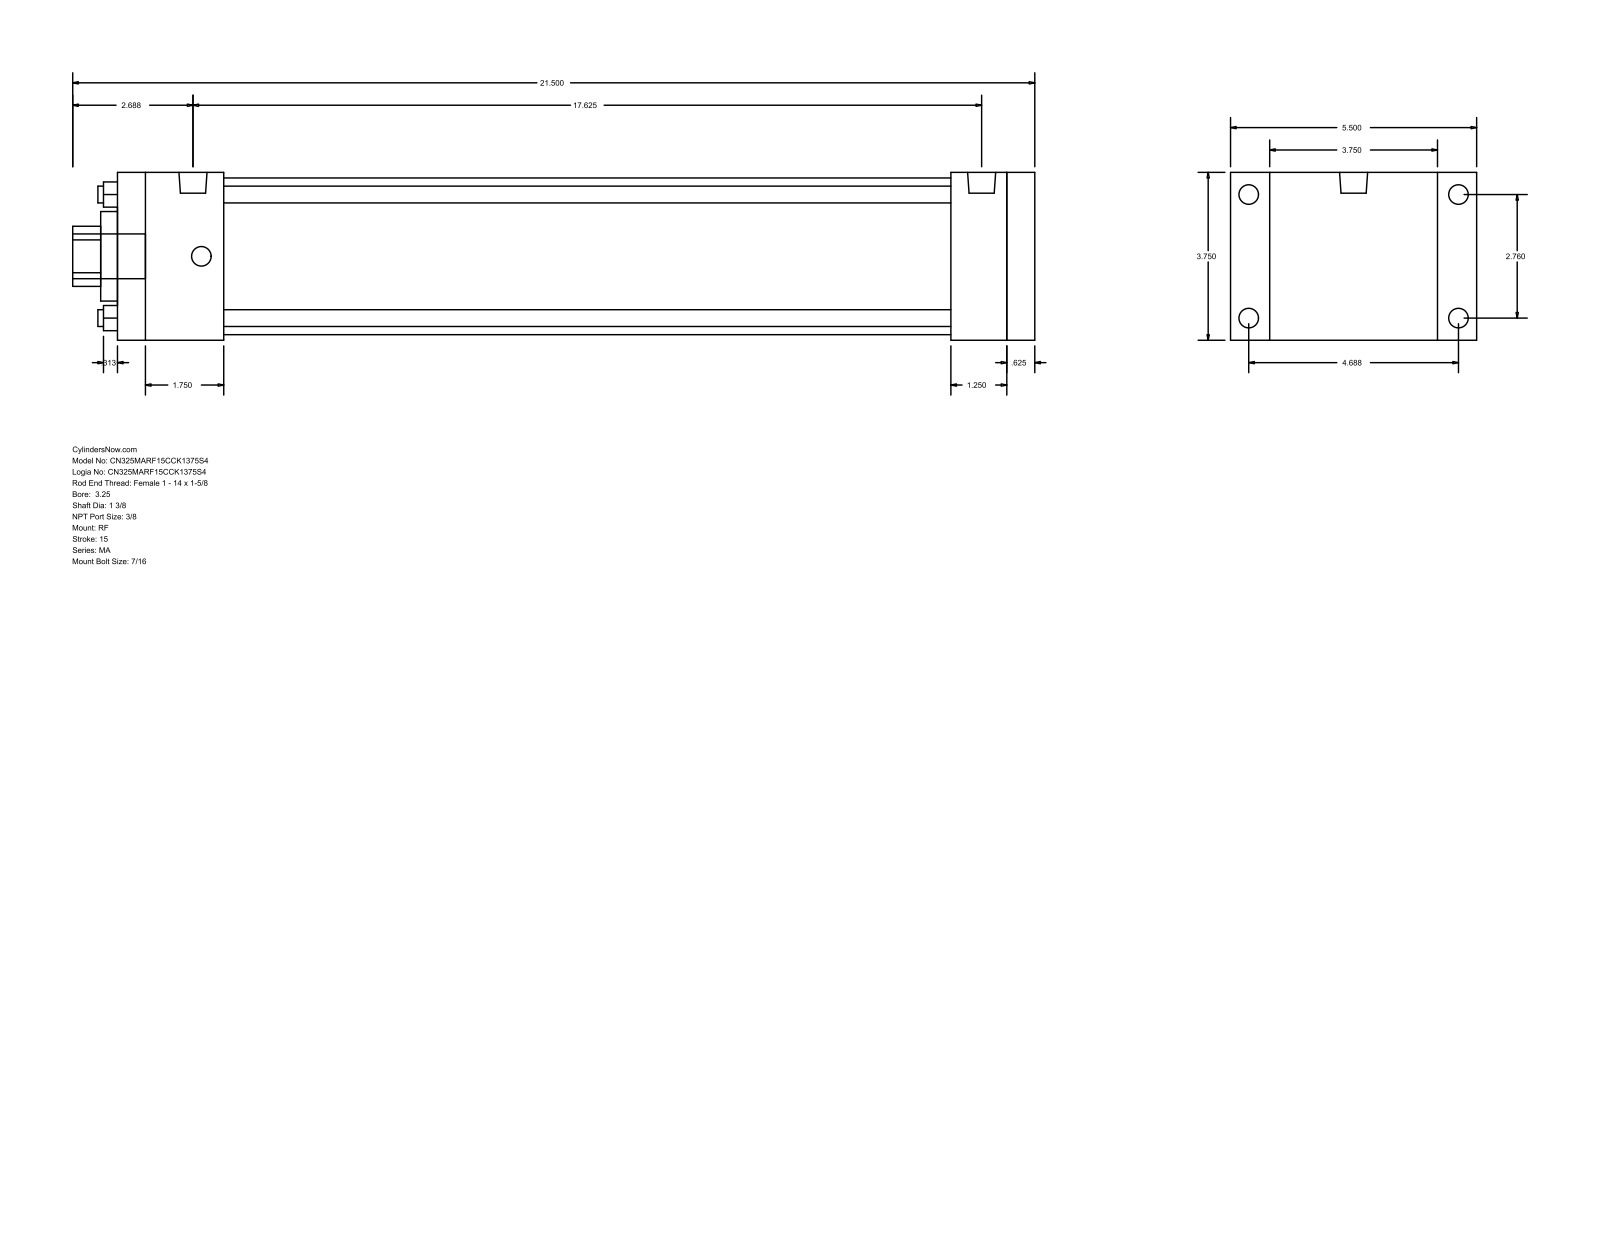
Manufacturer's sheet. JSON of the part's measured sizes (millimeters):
{"part_name": "MA_RF__0325_1.375", "step_written_by": "GSSL Pune (CONFIG_CONTROL_DESIGN)", "units": "millimeters", "bodies": {"solids": 0, "faces": 92, "planar": 64, "cylindrical": 28, "other": 0}, "overall_size": [546.1, 139.7, 95.25], "round_holes": [[9.53, 4], [34.92, 1], [50.8, 1], [88.9, 1]], "round_bosses_or_shafts": [[11.11, 8], [15.93, 2], [25.4, 1]], "partial_cylinders_radius": [[17.06, 1]], "face_to_face_distances": [95.24, 520.7, 15.87, 504.83, 22.23, 117.47, 473.08, 31.75, 47.62, 60.32], "hole_center_spacings": [49.57, 70.1, 99.14]}
